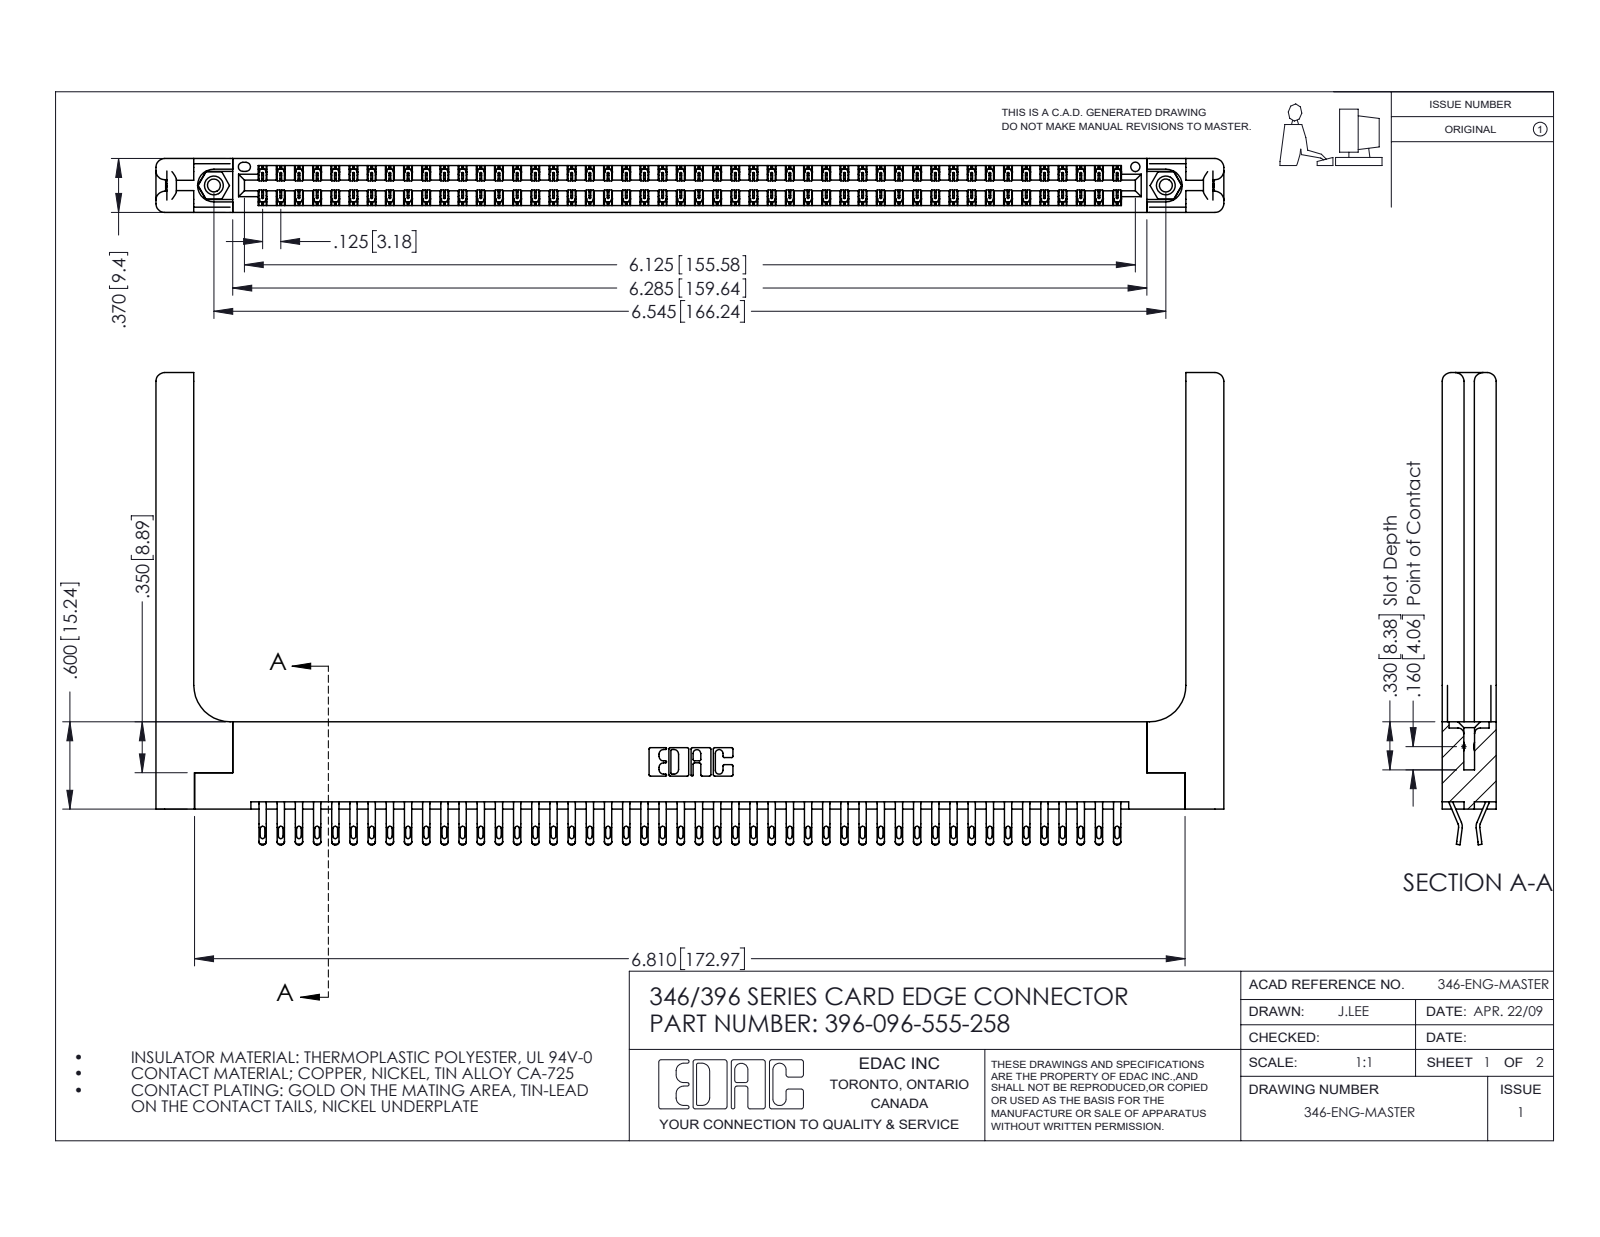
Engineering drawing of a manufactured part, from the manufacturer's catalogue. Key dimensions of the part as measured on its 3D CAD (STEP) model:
Part name (STEP PRODUCT): 345-250-001_345-250-001-102; 345-292-001_555 Tail; 346 Part_Flush Mounting Lugs - 0.156 Dia-TH; 396-096-555-258 (+1 more)
STEP written by: SolidWorks 2016 (CONFIG_CONTROL_DESIGN)
Units: inches
Bodies: 101 solids, 5946 faces (3392 planar, 2494 cylindrical, 60 other)
Overall size (bounding box): 7.341 × 3.245 × 0.37
Volume: 1.587 in³ · Surface area: 48.82 in²
Round holes (diameter × count): ⌀0.089 ×2, ⌀0.125 ×2, ⌀0.156 ×2, ⌀0.064 ×1
Round bosses / shafts (diameter × count): ⌀0.155 ×2
Partial cylindrical surfaces — rounded edges, fillets, slot ends (radius × count): R0.016 ×192, R0.02 ×192, R0.006 ×144, R0.01 ×22, R0.06 ×16, R0.007 ×6, R0.031 ×6, R0.026 ×3
Main face-to-face distances: 0.37, 0.048, 0.322, 0.072, 0.148, 0.15, 0.25, 0.025, 0.298, 0.275
Hole centre spacings: 0.246, 6.336, 6.545
